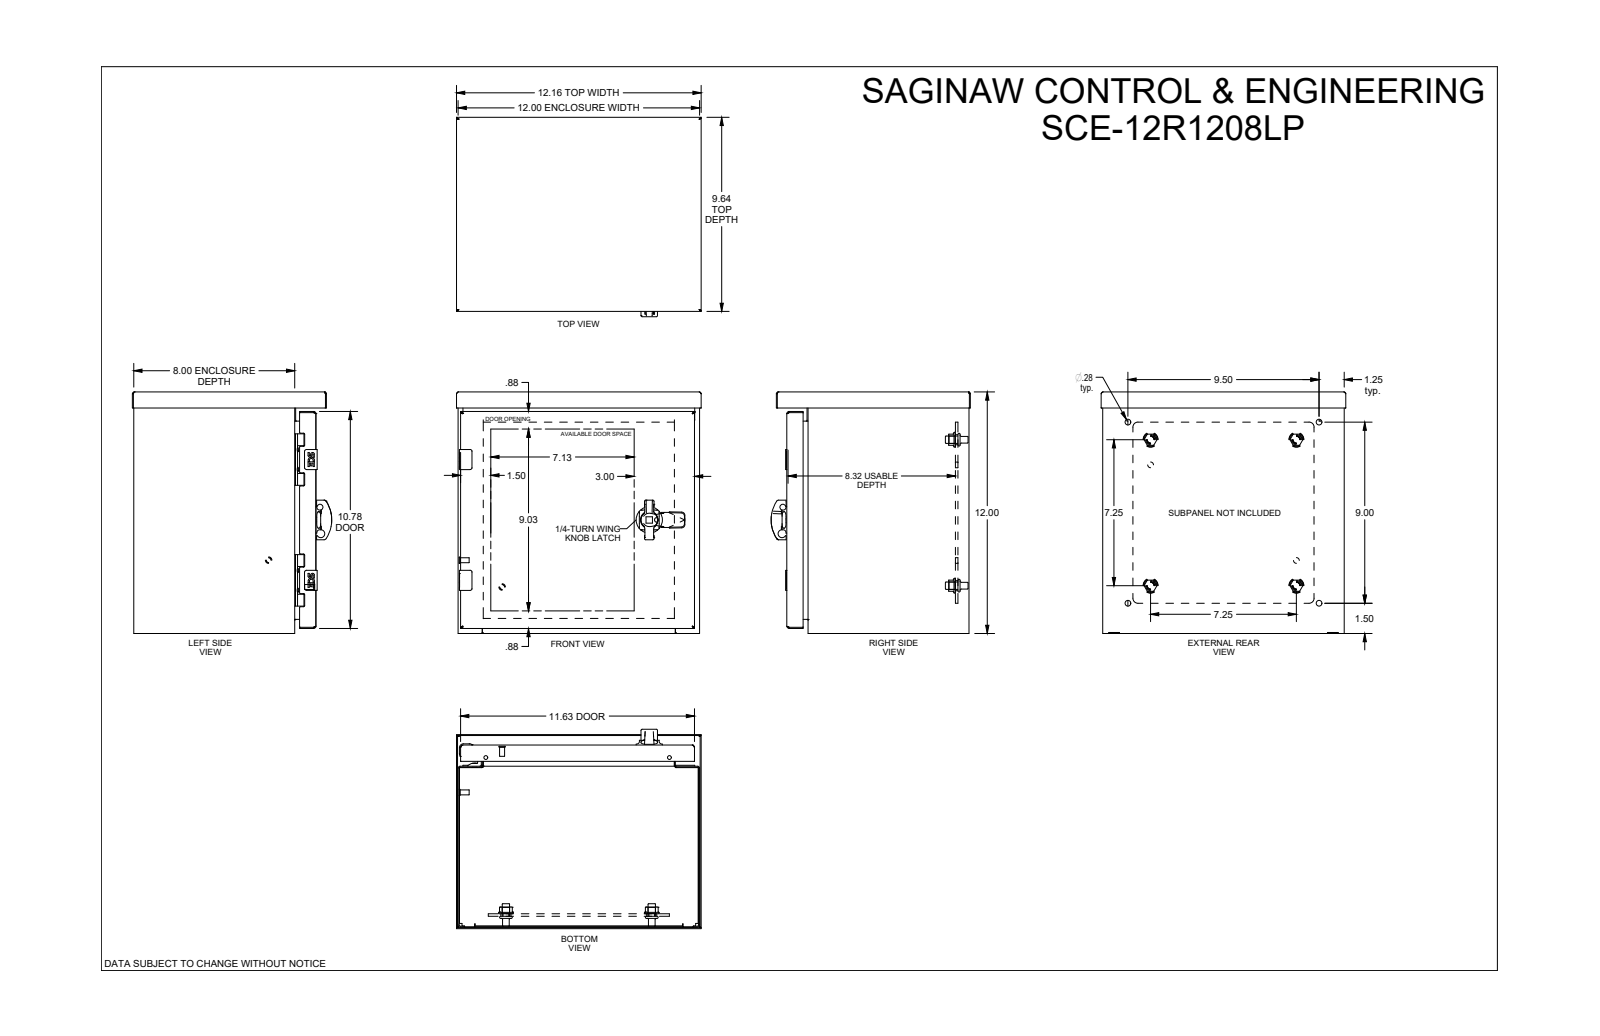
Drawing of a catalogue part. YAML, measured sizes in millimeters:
part_name: "SCE-12R1208LP"
step_written_by: "SolidWorks 2019 (AUTOMOTIVE_DESIGN)"
units: millimeters
bodies: {solids: 37, faces: 1560, planar: 744, cylindrical: 500, other: 316}
overall_size: [308.8, 304.9, 251.6]
volume: 1147000
surface_area: 1278000
round_holes:
  - {diameter: 4.4, count: 4}
  - {diameter: 5.2, count: 4}
  - {diameter: 6.2, count: 4}
  - {diameter: 6.8, count: 4}
  - {diameter: 7.1, count: 4}
  - {diameter: 9.3, count: 4}
  - {diameter: 9.5, count: 4}
  - {diameter: 12.7, count: 4}
  - {diameter: 1, count: 2}
  - {diameter: 4.8, count: 2}
  - {diameter: 5.5, count: 2}
  - {diameter: 7.1, count: 2}
round_bosses_or_shafts:
  - {diameter: 4.3, count: 6}
  - {diameter: 9.3, count: 4}
  - {diameter: 8.4, count: 4}
  - {diameter: 6.4, count: 4}
  - {diameter: 6.1, count: 4}
  - {diameter: 5, count: 3}
  - {diameter: 6.3, count: 2}
  - {diameter: 33.1, count: 1}
partial_cylinders:
  - {radius: 0.4, count: 36}
  - {radius: 0.3, count: 30}
  - {radius: 0.3, count: 28}
  - {radius: 1.5, count: 17}
  - {radius: 0.5, count: 12}
  - {radius: 1.6, count: 10}
  - {radius: 2.5, count: 8}
  - {radius: 5.6, count: 8}
face_to_face_distances: [1.5, 303.3, 303.3, 228.4, 226.9, 1.5, 229.9, 228.4, 304.8, 301.8]
hole_center_spacings: [152.4, 224.8, 0.3, 0.3, 12.3, 12.5, 12.5, 12.7]
